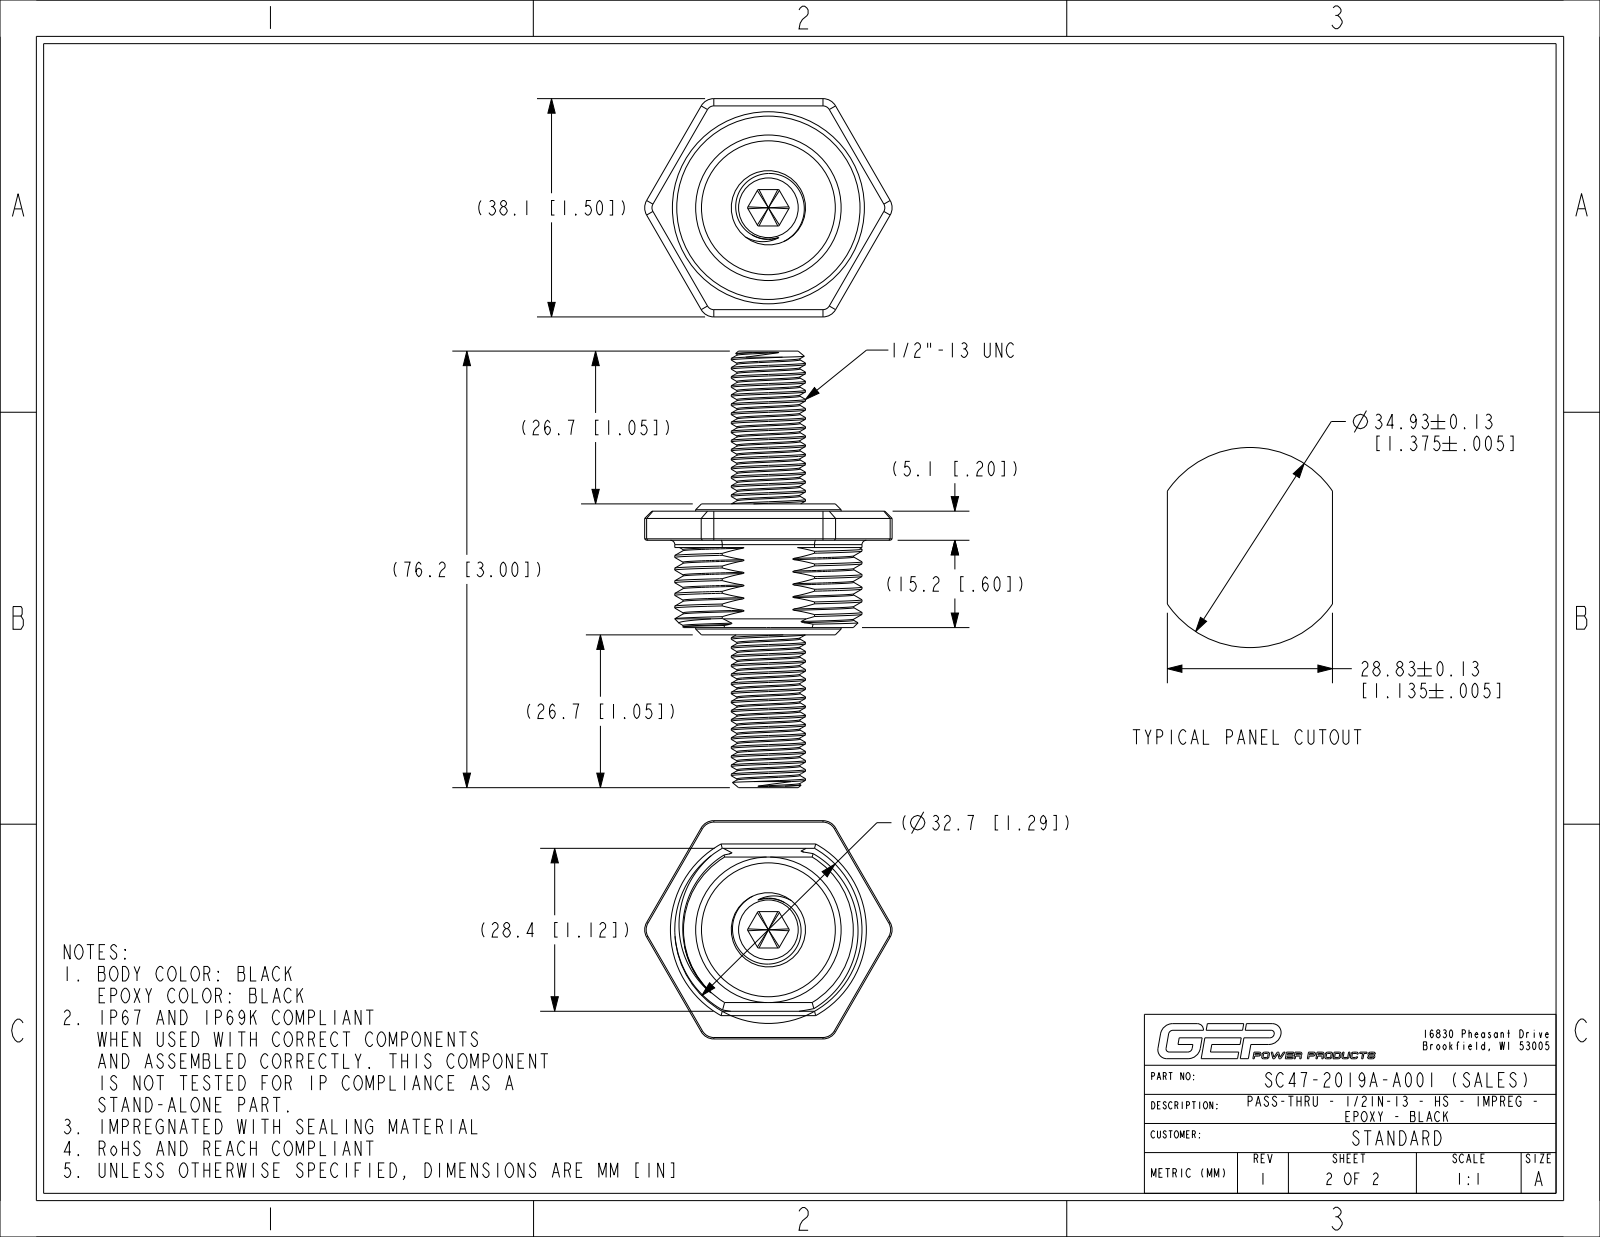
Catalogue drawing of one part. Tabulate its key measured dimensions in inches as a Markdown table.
| quantity | value |
| --- | --- |
| part name | C07-1002_NCF; PC40-2005A-B001_MOLD_NCF; PC40-2005A-B001_NCF_ASM; PC05-2016A-A000_NCF (+6 more) |
| STEP written by | CREO PARAMETRIC BY PTC INC, 2024014 (CONFIG_CONTROL_DESIGN) |
| units | inches |
| bodies | 5 solids, 625 faces (286 planar, 169 cylindrical, 170 other) |
| overall size | 3 × 1.701 × 1.5 |
| volume | 1.475 in³ |
| surface area | 26.8 in² |
| round holes (diameter × count) | 0.422 × 1, 0.84 × 1, 1.26 × 1 |
| round bosses / shafts (diameter × count) | 1.26 × 1, 1 × 1, 0.51 × 1 |
| partial cylindrical surfaces (radius × count) | 0.1 × 6, 0.181 × 6, 0.03 × 2, 0.644 × 1 |
| main face-to-face distances | 0.574, 0.573, 0.05, 0.25, 0.85, 0.08, 0.17, 0.65, 0.73, 0.9 |
